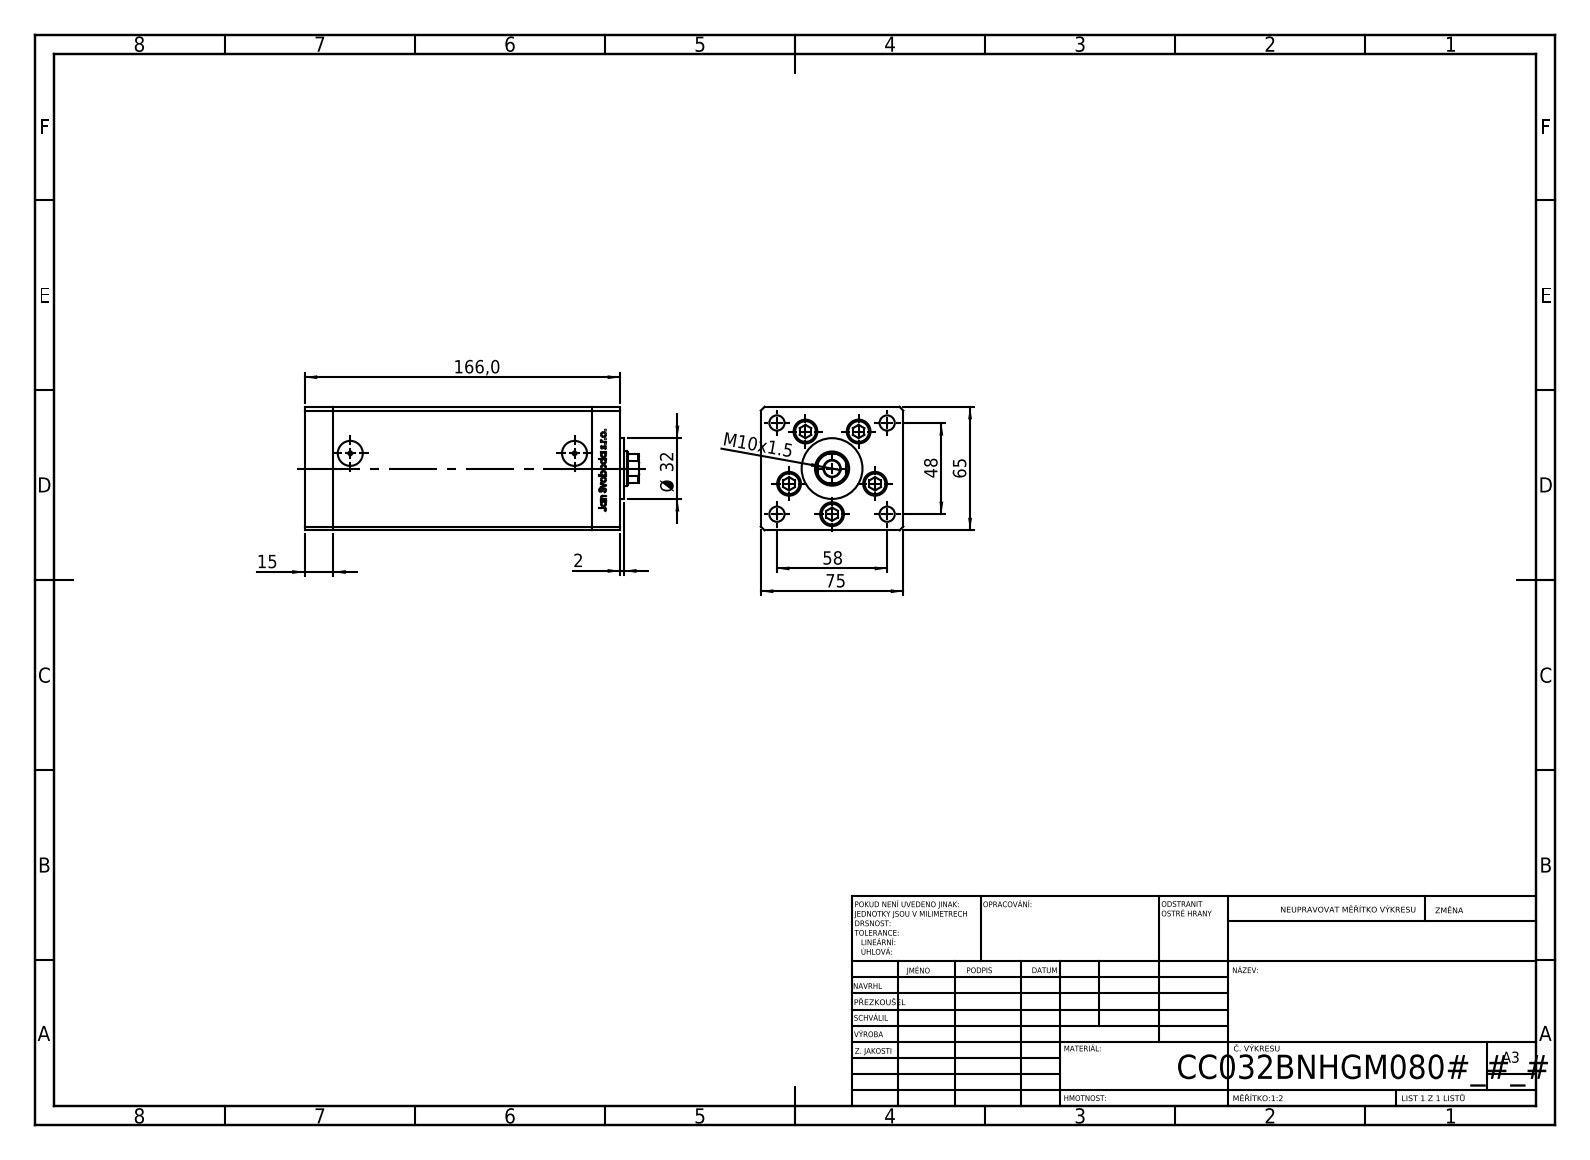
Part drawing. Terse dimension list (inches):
name: V220C_VC_B; ALLEN BOLT; V220C BACK_B; V220C_B MIDDLE (+1 more)
written by: SolidWorks 2019 (CONFIG_CONTROL_DESIGN)
unit: in
bodies: 14 solids, 1183 faces (462 planar, 147 cylindrical, 574 other)
size: 6.929 × 2.953 × 2.559
volume: 44.09 in³; area: 197.4 in²
holes: 5× ⌀0.354, 5× ⌀0.492, 4× ⌀0.315, 2× ⌀0.079, 2× ⌀0.518, 1× ⌀0.335, 1× ⌀0.709
bosses: 5× ⌀0.315, 1× ⌀1.26
rounds: 2× R0.037, 1× R0.335
face distances: 2.953, 2.559, 0.591, 5.354, 5.945, 6.535, 1.102, 0.512, 2.146, 0.413
hole spacings: 0.945, 1.482, 0.617, 0.678, 1.091, 1.135, 1.142, 1.285
